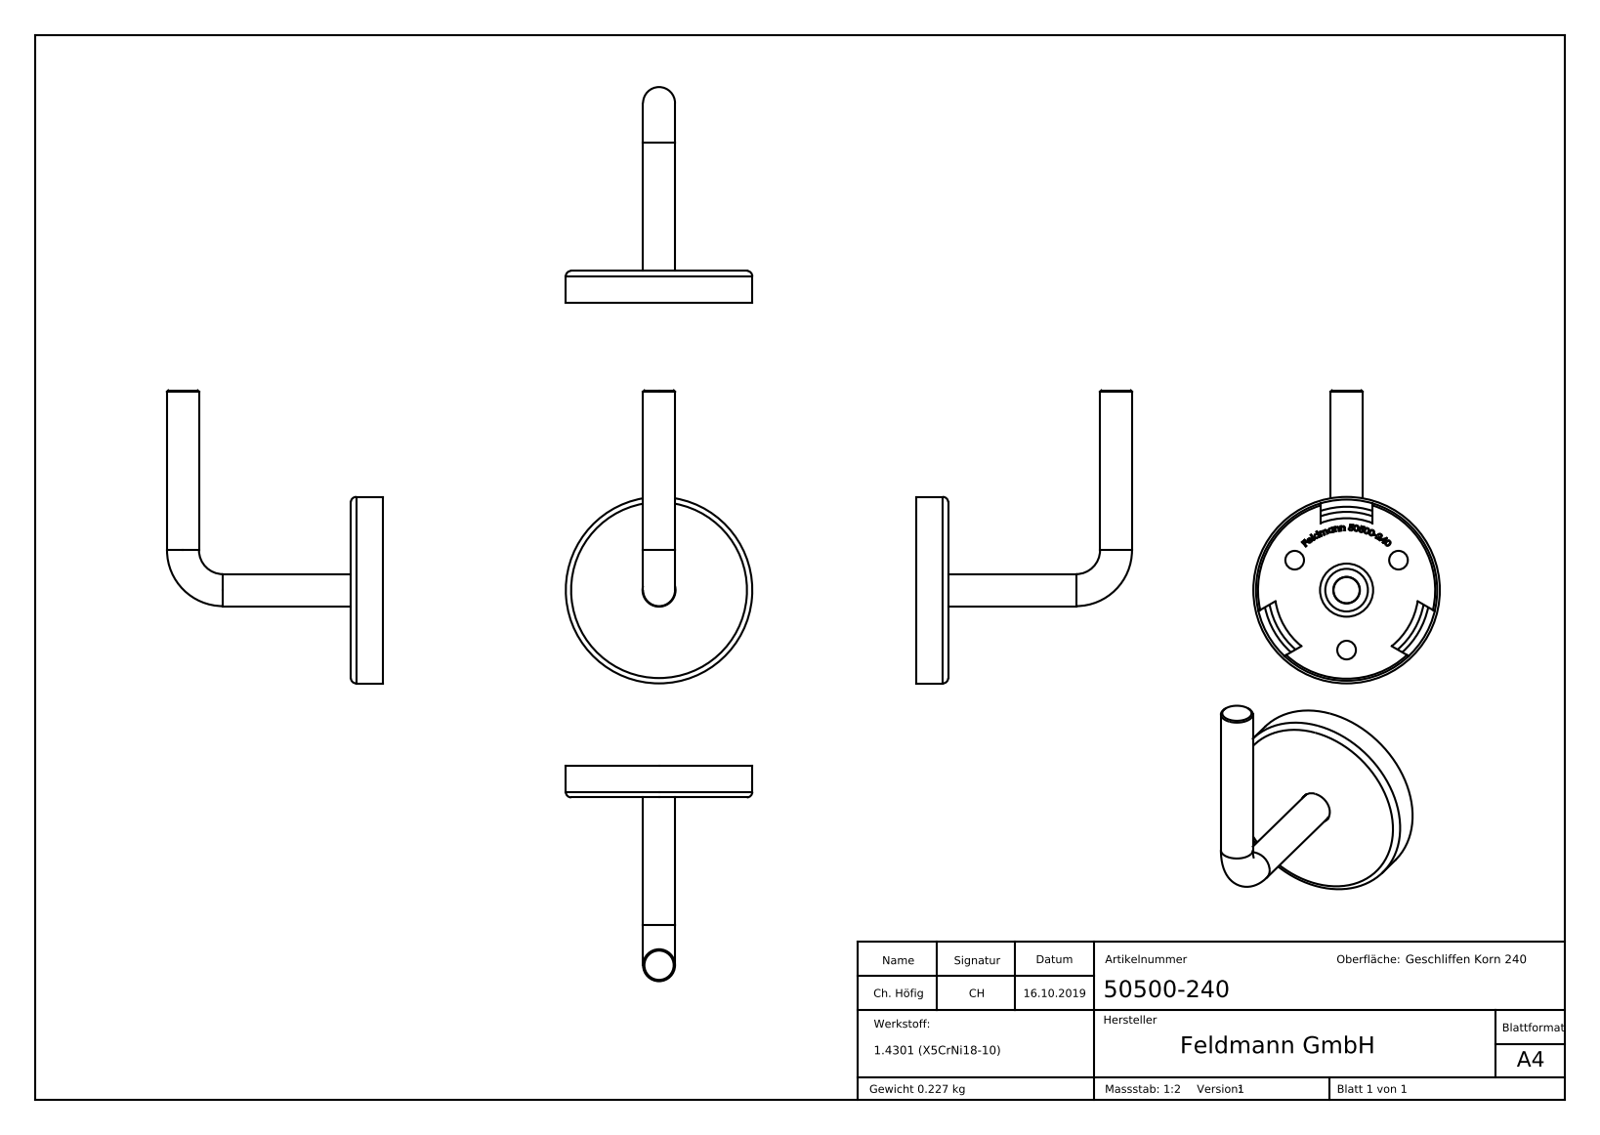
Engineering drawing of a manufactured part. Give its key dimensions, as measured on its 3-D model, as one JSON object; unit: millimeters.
{"part_name": "5050X-240 Teil2; 5050X-240 Teil1_50500-240-P; 5050X-240 Teil3; 5050X-240 Teil2_50500-240 Teil2 (+3 more)", "step_written_by": "SolidWorks 2015 (CONFIG_CONTROL_DESIGN)", "units": "millimeters", "bodies": {"solids": 3, "faces": 282, "planar": 140, "cylindrical": 16, "other": 126}, "overall_size": [110, 81, 70], "volume_mm3": 28755, "surface_area_mm2": 25401, "round_holes": [[7, 3], [10, 1], [12.4, 1]], "round_bosses_or_shafts": [[12, 2], [70, 1], [68, 1], [9.8, 1]], "partial_cylinders_radius": [[33.25, 1]], "face_to_face_distances": [1, 11, 12, 2, 9, 10, 3.2, 1.2, 7.8, 8.8], "hole_center_spacings": [22.5, 38.97, 38.98]}
